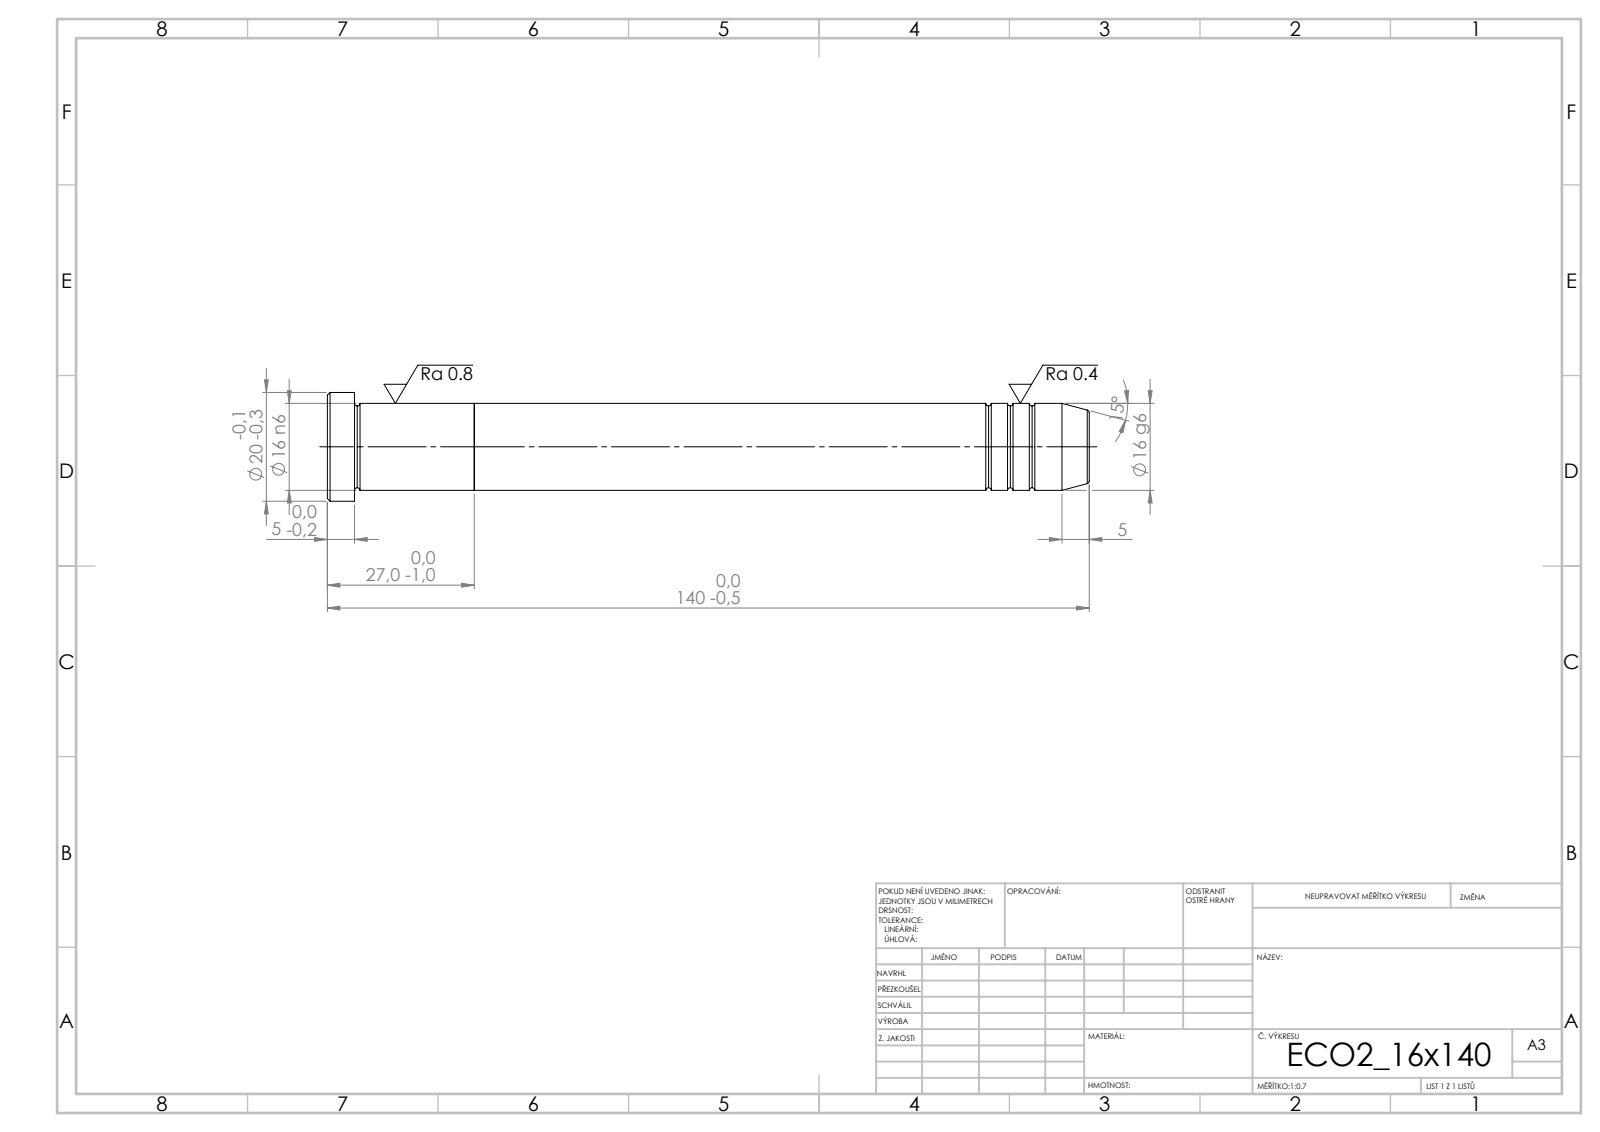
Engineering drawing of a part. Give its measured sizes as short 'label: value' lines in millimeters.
written by: SolidWorks 2019 (CONFIG_CONTROL_DESIGN)
unit: mm
bodies: 2 solids, 39 faces (5 planar, 12 cylindrical, 22 other)
size: 140 × 20 × 20
volume: 28 469 mm³; area: 8 134 mm²
bosses: 1× ⌀20, 1× ⌀16
face distances: 27, 113, 140, 135, 22, 5
